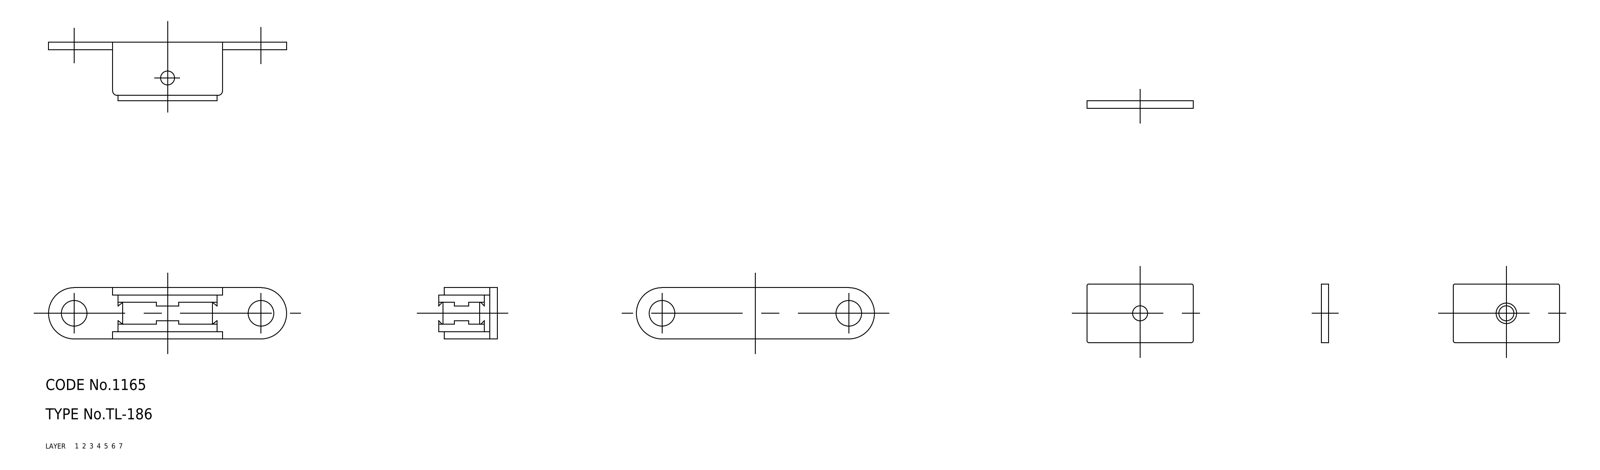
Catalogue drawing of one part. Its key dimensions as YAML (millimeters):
part_name: "attachment; magnet; keeper; housing (+1 more)"
step_written_by: "CADfix (AUTOMOTIVE_DESIGN)"
units: millimeters
bodies: {solids: 5, faces: 104, planar: 0, cylindrical: 0, other: 104}
overall_size: [65, 38.63, 16]
volume: 6711
surface_area: 7299
